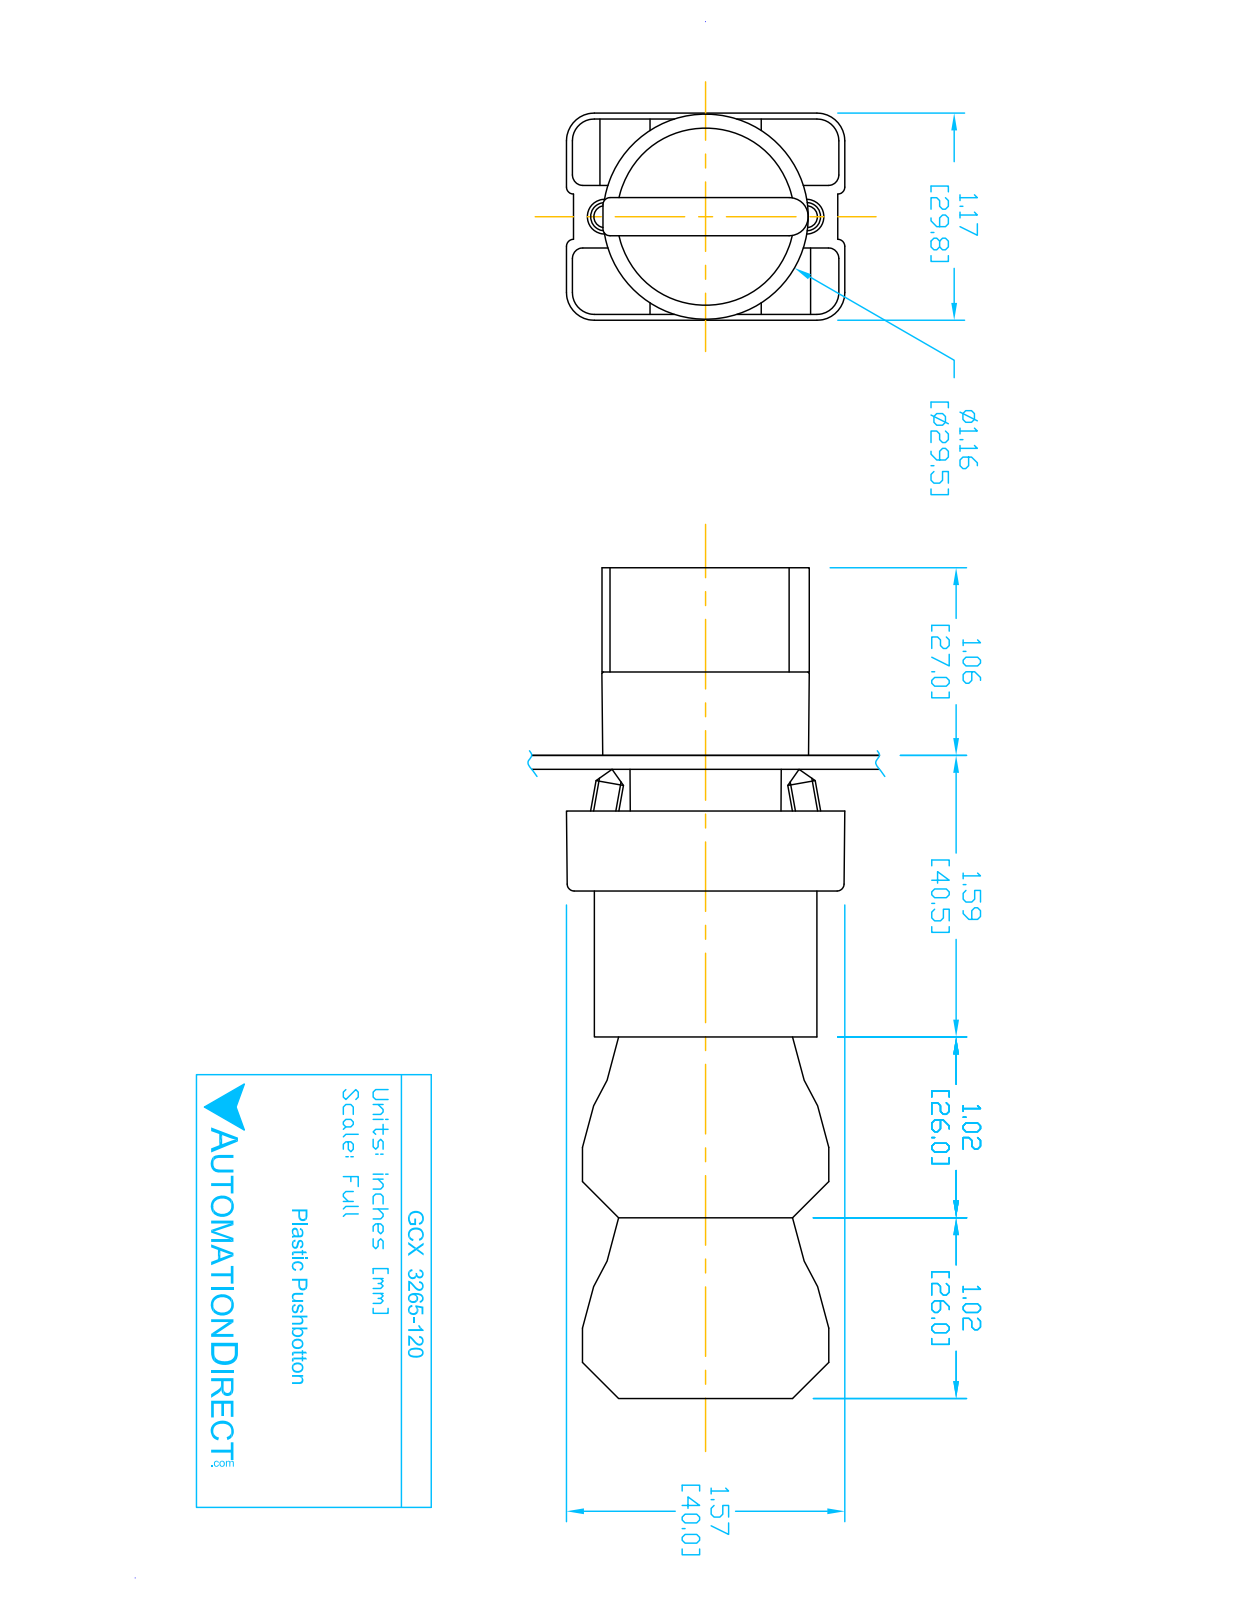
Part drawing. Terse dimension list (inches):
name: GCX3265-120; GCX3265 OPERATOR; ecx1040; ECX3029-2 (+2 more)
written by: SolidWorks 2016 (AUTOMOTIVE_DESIGN)
unit: in
bodies: 11 solids, 724 faces (488 planar, 193 cylindrical, 43 other)
size: 4.677 × 1.581 × 1.177
volume: 4.751 in³; area: 59.22 in²
holes: 4× ⌀0.079, 2× ⌀0.087, 2× ⌀0.124, 2× ⌀0.13, 1× ⌀0.197, 1× ⌀0.469, 1× ⌀0.878, 1× ⌀0.888, 1× ⌀1.024
bosses: 4× ⌀0.157, 1× ⌀1.175, 1× ⌀1.004, 1× ⌀0.945, 1× ⌀0.856, 1× ⌀0.78, 1× ⌀0.504
rounds: 24× R0.059, 12× R0.041, 12× R0.124, 12× R0.157, 9× R0.039, 2× R0.02, 2× R0.063, 2× R0.079
face distances: 0.579, 0.593, 1.024, 1.171, 0.014, 0.827, 1.85, 3.043, 2.02, 1.193
hole spacings: 0.236, 1.003, 0.974, 0.472, 0.539, 0.544, 1.083, 0.484
